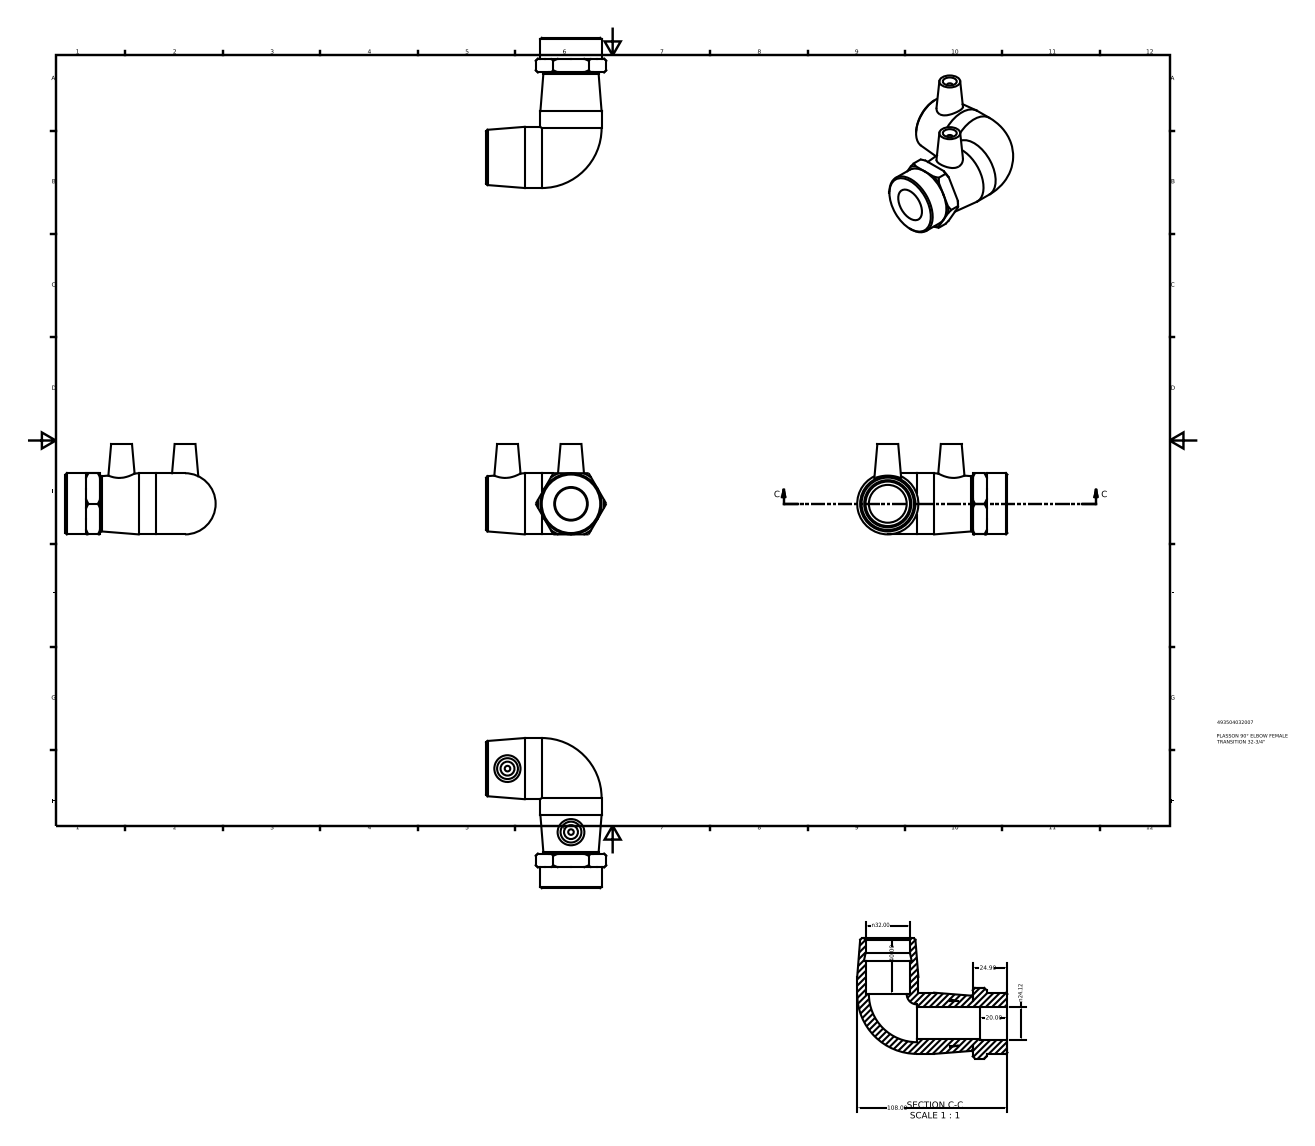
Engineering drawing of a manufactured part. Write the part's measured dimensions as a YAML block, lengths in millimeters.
part_name: "493504032007"
step_written_by: "Autodesk Inventor 2015 (AUTOMOTIVE_DESIGN)"
units: millimeters
bodies: {solids: 1, faces: 64, planar: 27, cylindrical: 13, other: 24}
overall_size: [108, 86.4, 65]
volume: 132700
surface_area: 38312
round_holes:
  - {diameter: 10, count: 2}
  - {diameter: 23, count: 1}
  - {diameter: 24.12, count: 1}
  - {diameter: 32, count: 1}
round_bosses_or_shafts:
  - {diameter: 44, count: 2}
  - {diameter: 4, count: 2}
  - {diameter: 32, count: 1}
face_to_face_distances: [24.9, 44, 40, 65, 25, 21, 24, 16, 40.1, 51]
hole_center_spacings: [64.56]
